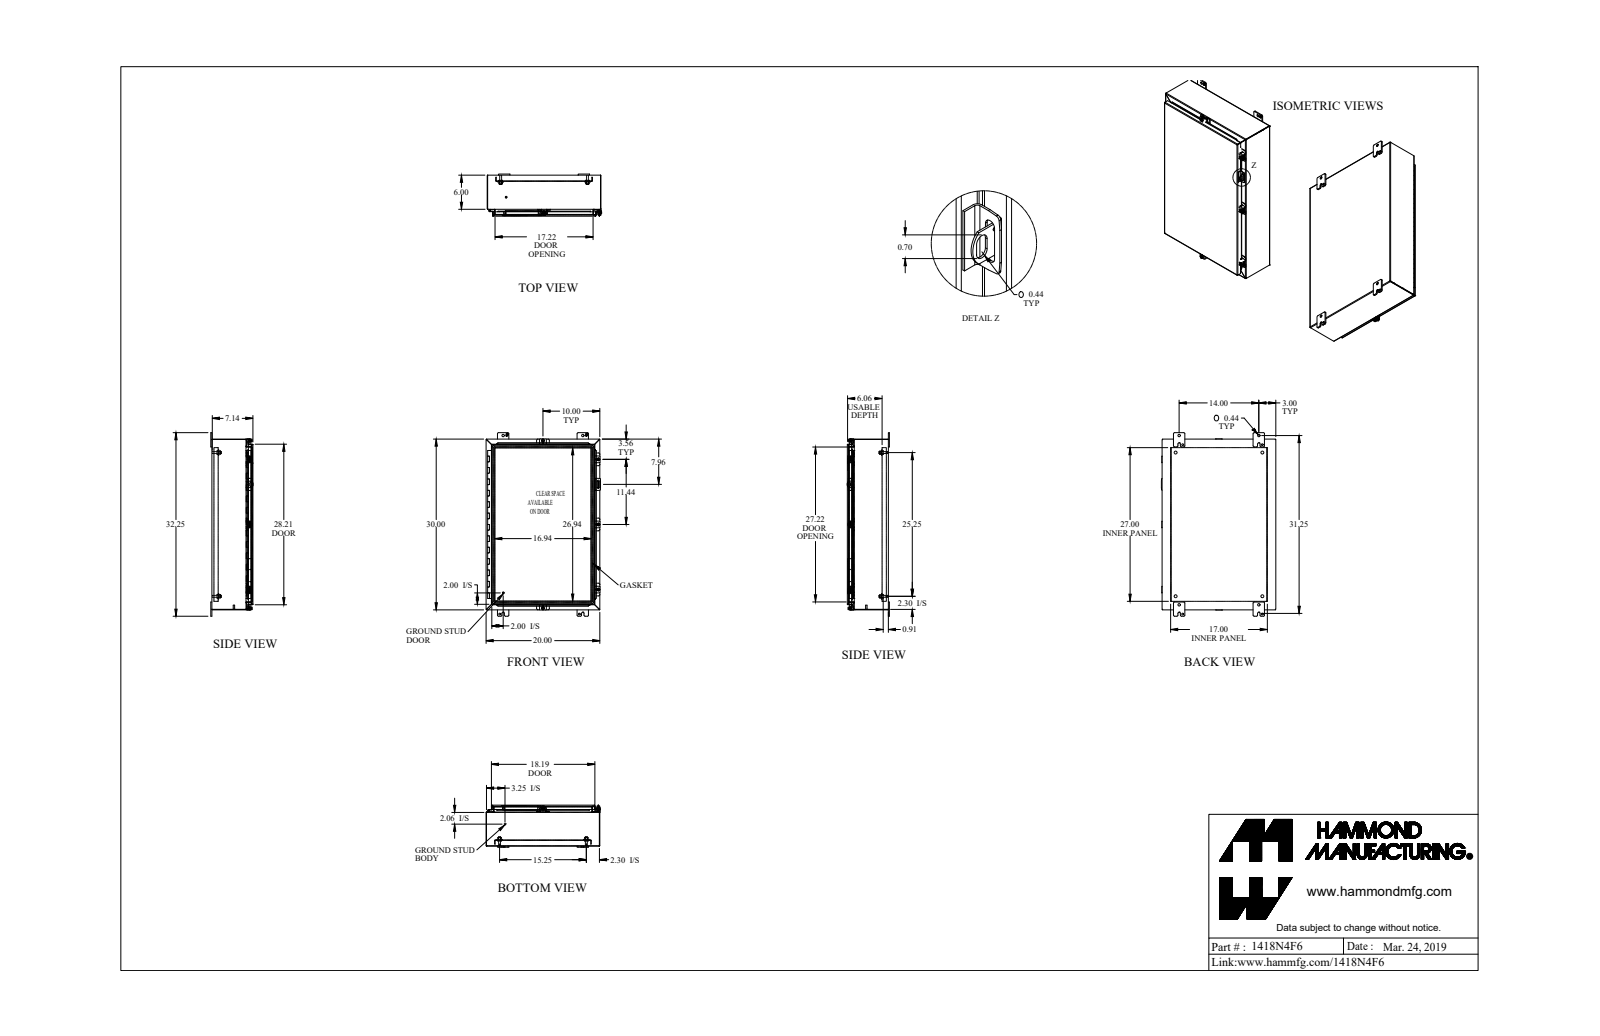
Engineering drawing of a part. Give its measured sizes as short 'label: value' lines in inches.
name: 1418N4F6_Default
written by: SolidWorks 2019 (CONFIG_CONTROL_DESIGN)
unit: in
bodies: 43 solids, 1600 faces (965 planar, 549 cylindrical, 86 other)
size: 32.25 × 20.126 × 7.437
volume: 210.8 in³; area: 5 496 in²
holes: 5× ⌀0.213, 5× ⌀0.375, 4× ⌀0.313, 4× ⌀0.437, 4× ⌀0.5, 3× ⌀0.265, 2× ⌀0.265, 2× ⌀0.307, 2× ⌀0.445, 1× ⌀0.125, 1× ⌀0.187
bosses: 5× ⌀0.5, 5× ⌀0.39, 5× ⌀0.244, 4× ⌀0.65, 4× ⌀0.375, 4× ⌀0.33, 2× ⌀1, 2× ⌀0.281
rounds: 27× R0.048, 27× R0.143, 26× R0.188, 24× R0.036, 24× R0.108, 24× R0.25, 10× R0.125, 10× R0.141
face distances: 0.072, 0.072, 7.066, 7.138, 7.138, 7.21, 0.095, 6.106, 6.034, 1.032
hole spacings: 29.498, 7.916, 28.417, 14, 21.478, 1.736, 2.434, 3.065
